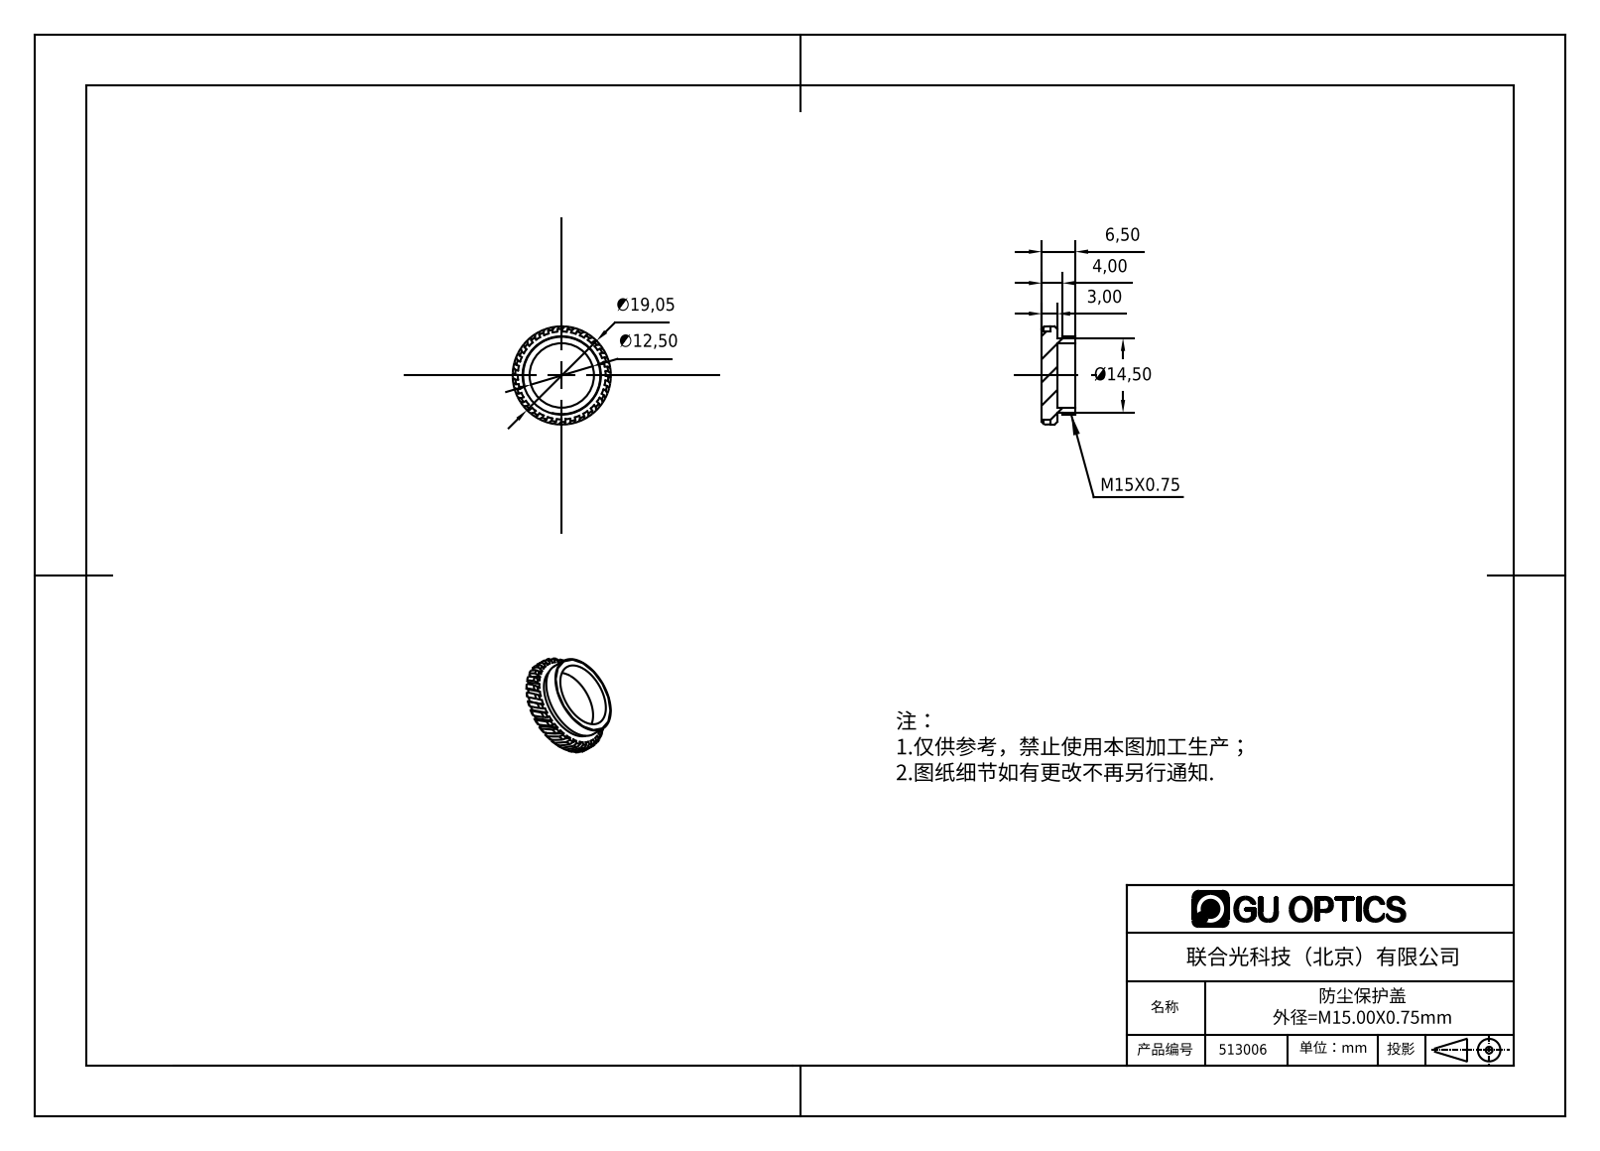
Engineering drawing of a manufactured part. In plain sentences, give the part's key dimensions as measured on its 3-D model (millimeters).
The part is named "513006". Its 3-D file was written by "SolidWorks 2016 (AUTOMOTIVE_DESIGN)". It is 1 solid with 224 faces: 65 planar, 97 cylindrical and 62 other. Overall it measures 19.05 by 19.05 by 6.5 millimeters. Its volume is 951 cubic millimeters and its surface area 1 205 square millimeters. Round holes: 1 of diameter 12.5. Round bosses or shafts: 1 of diameter 19.05, 1 of diameter 17.05, 1 of diameter 15.2, 1 of diameter 14.5. The main face-to-face distances are 3, 0.8, 3.5, 6.5, 2.5, 1, 4, 0.79.
